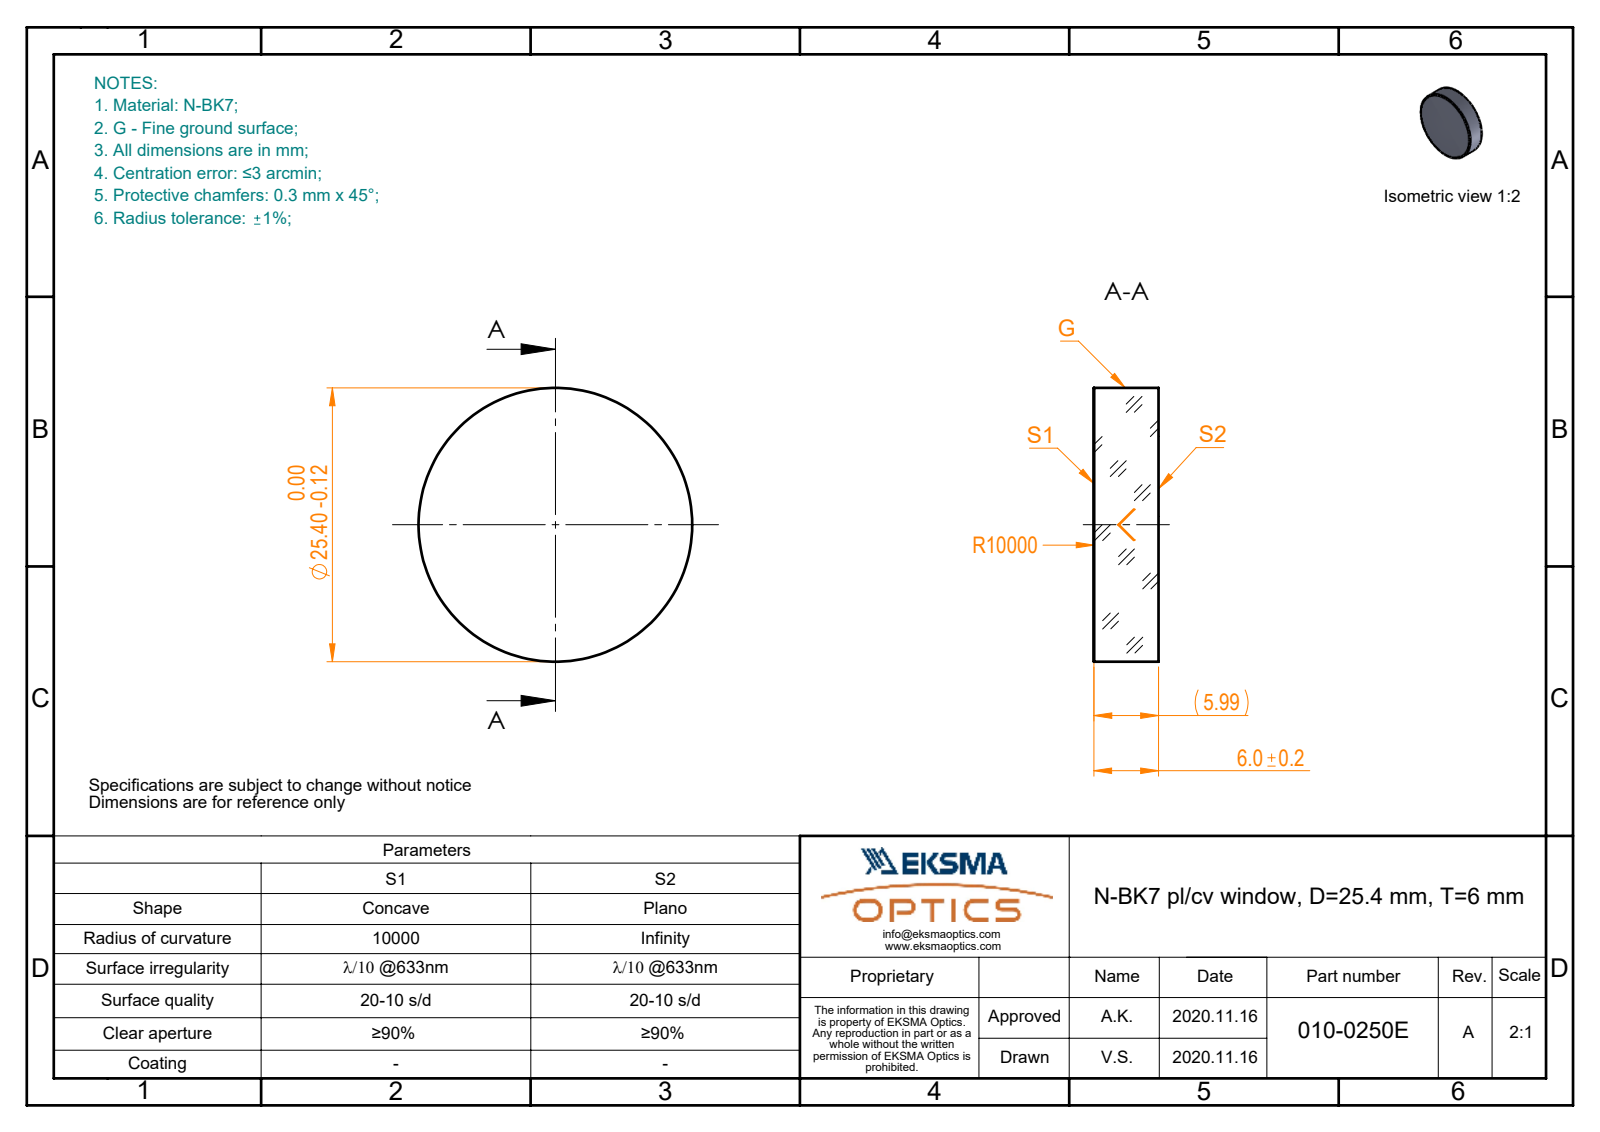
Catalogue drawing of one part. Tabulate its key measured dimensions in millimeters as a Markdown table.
| quantity | value |
| --- | --- |
| part name | 010-0250E_N-BK7_PCV_window |
| STEP written by | SolidWorks 2019 (CONFIG_CONTROL_DESIGN) |
| units | millimeters |
| bodies | 1 solid, 5 faces (1 planar, 2 cylindrical, 2 other) |
| overall size | 25.4 × 25.4 × 6 |
| volume | 3 038 mm³ |
| surface area | 1 492 mm² |
| round bosses / shafts (diameter × count) | 25.4 × 1 |
